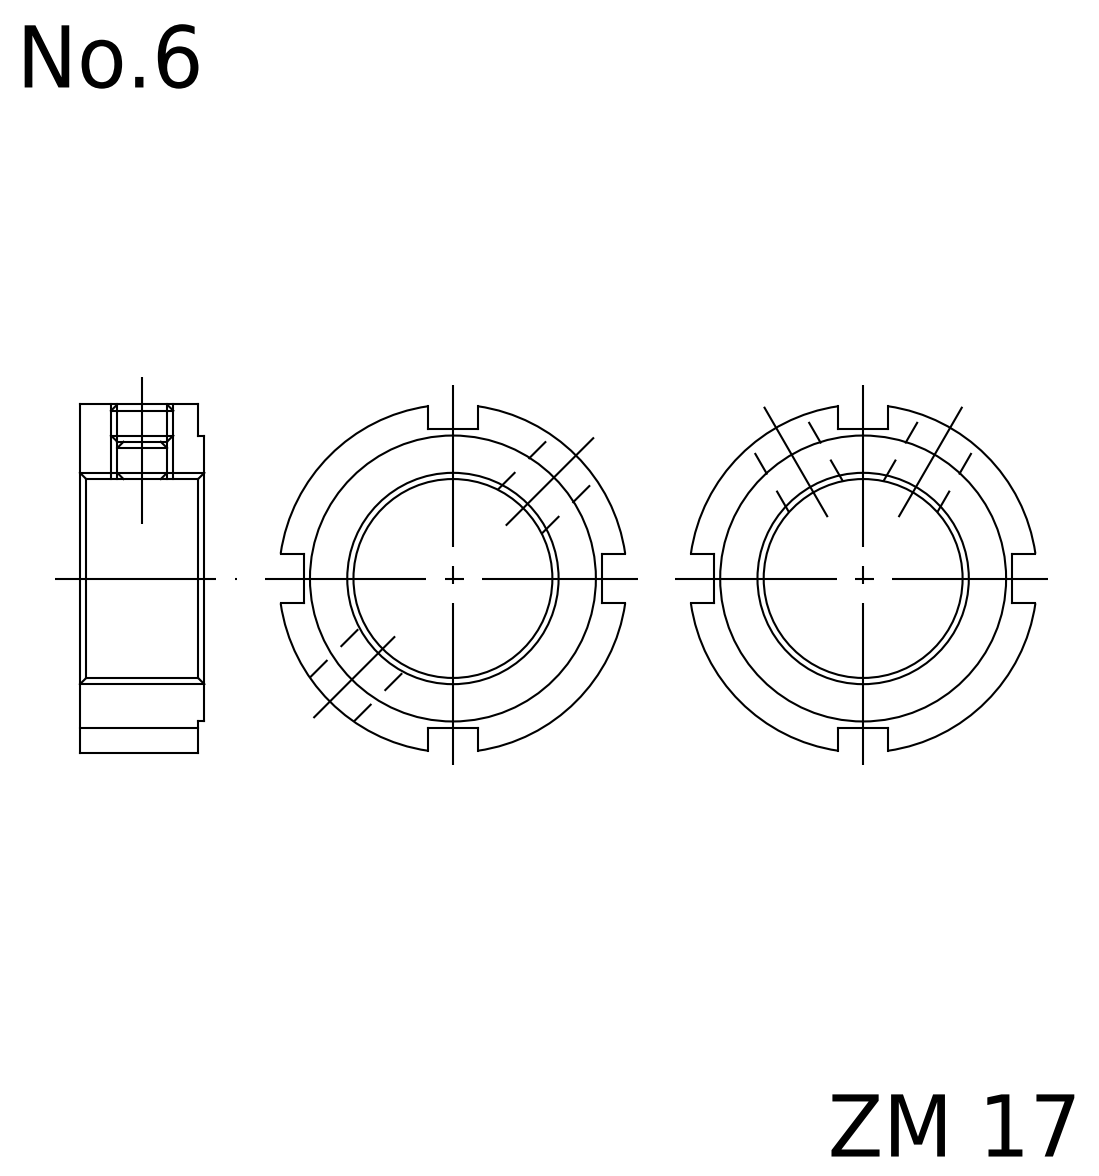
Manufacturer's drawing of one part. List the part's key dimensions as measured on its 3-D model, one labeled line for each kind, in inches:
Part name (STEP PRODUCT): FKD ZM 17
STEP written by: Autodesk Inventor 2011 (AUTOMOTIVE_DESIGN)
Units: inches
Bodies: 1 solid, 23 faces (15 planar, 8 cylindrical, 0 other)
Overall size (bounding box): 1.091 × 1.091 × 0.394
Volume: 0.204 in³ · Surface area: 3.646 in²
Round holes (diameter × count): ⌀0.163 ×2, ⌀0.669 ×1
Round bosses / shafts (diameter × count): ⌀1.102 ×1, ⌀0.906 ×1
Main face-to-face distances: 0.394, 0.02, 0.374, 0.551, 0.945, 0.157
